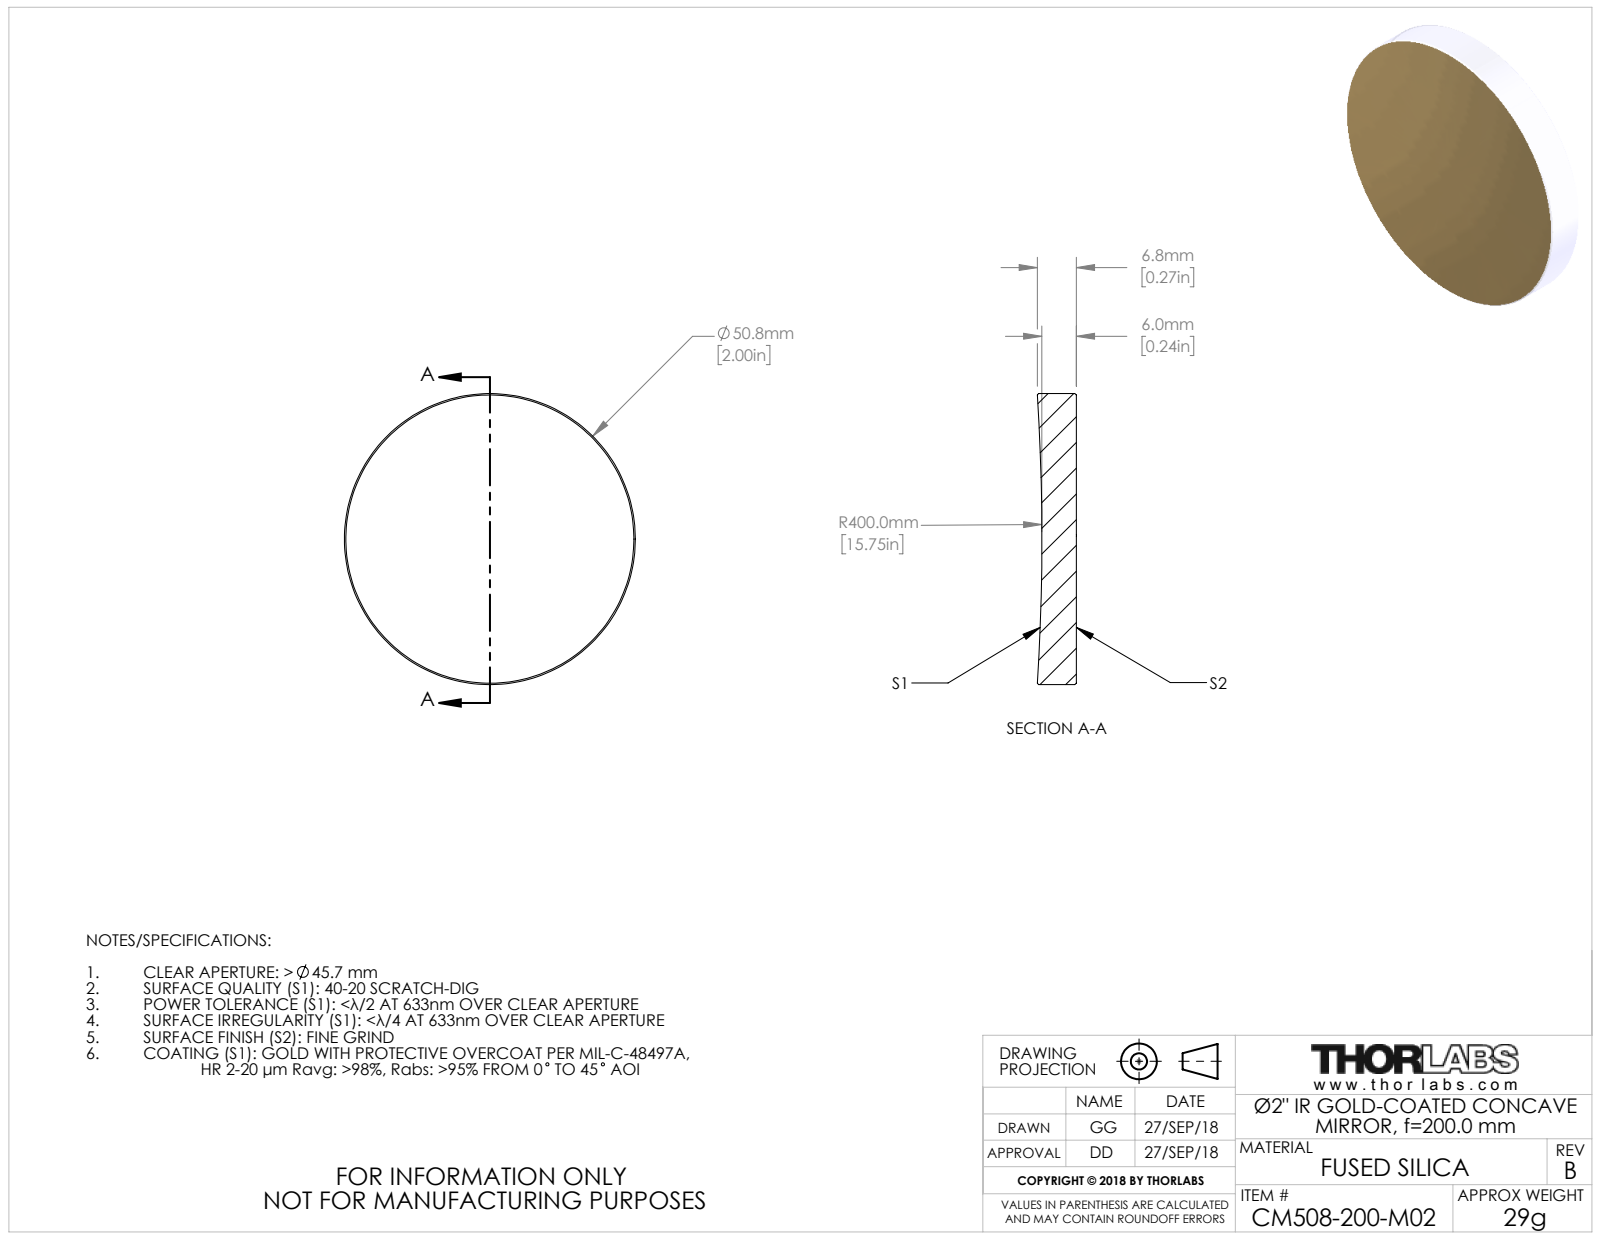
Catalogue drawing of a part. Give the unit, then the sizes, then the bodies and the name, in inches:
Units: inches
Overall size (bounding box): 2 × 2 × 0.267
Round bosses / shafts (diameter × count): ⌀2 ×1
Volume: 0.791 in³ · Surface area: 7.896 in²
Bodies: 1 solid, 41 faces (33 planar, 2 cylindrical, 6 other)
Part name (STEP PRODUCT): TTN028025-E0W
STEP written by: SolidWorks 2018 (AUTOMOTIVE_DESIGN)
